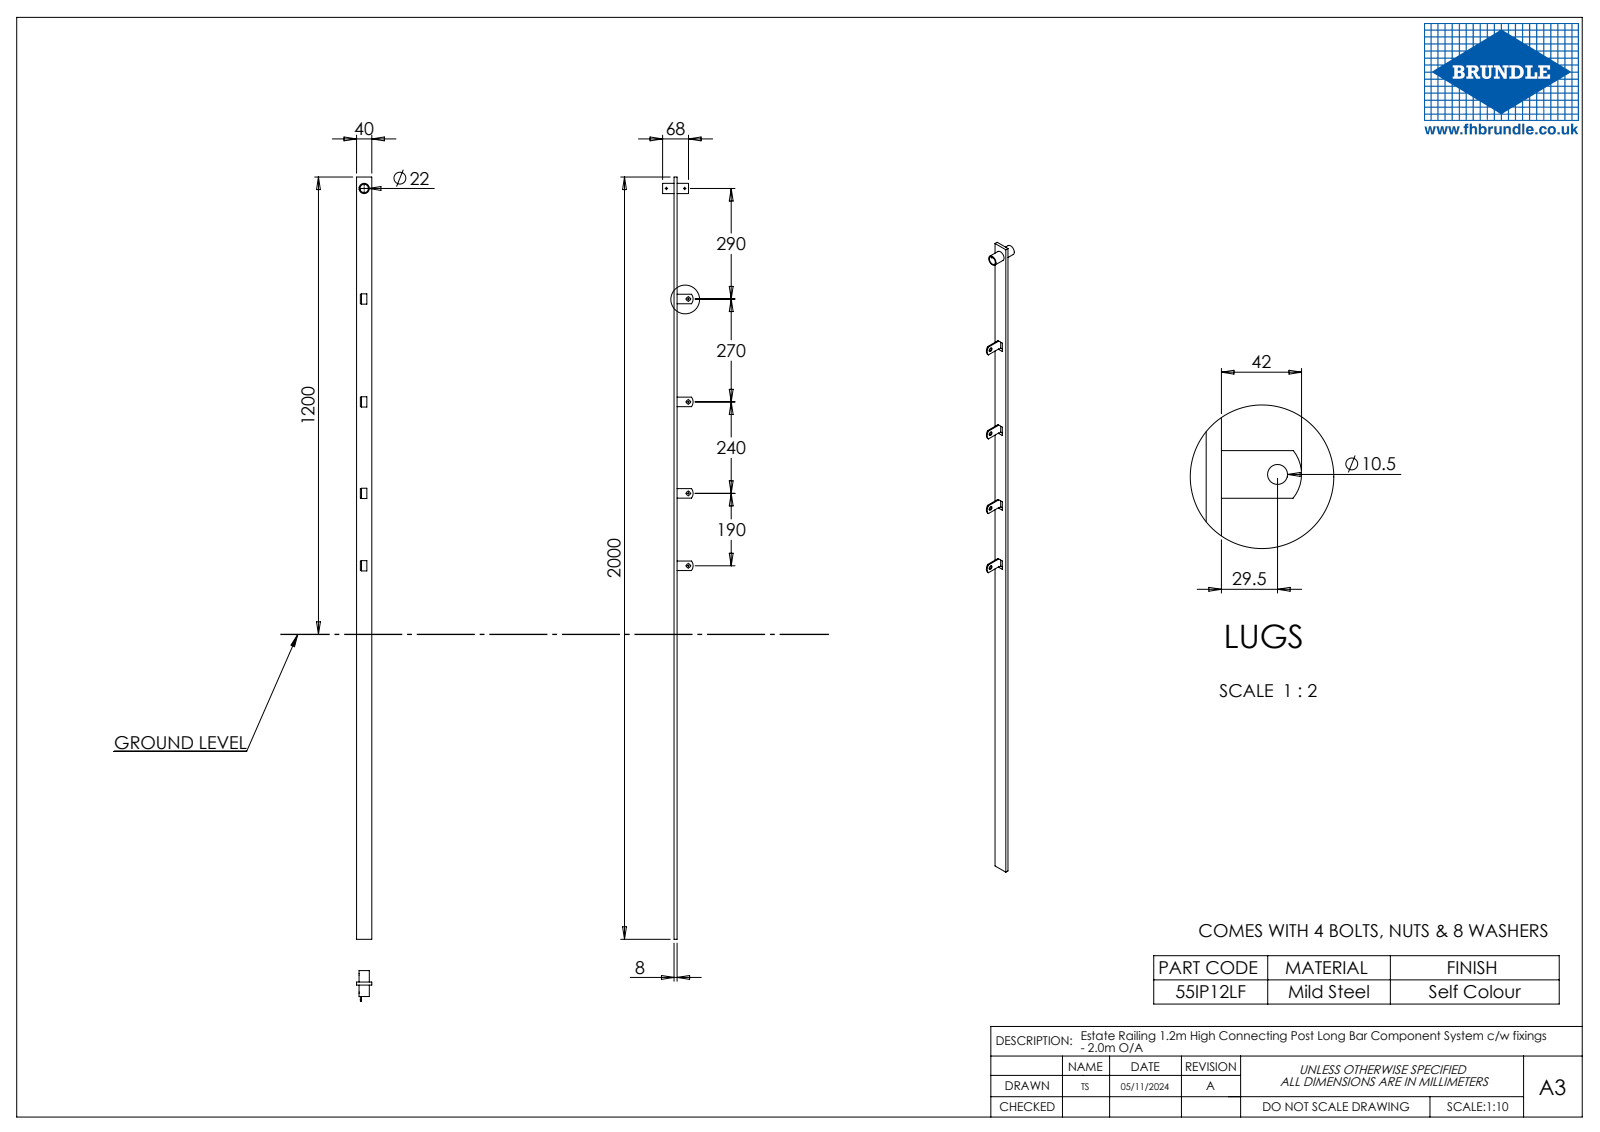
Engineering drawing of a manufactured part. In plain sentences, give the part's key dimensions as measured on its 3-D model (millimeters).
The part is named "65IP12L". Its 3-D file was written by "SolidWorks 2020 (CONFIG_CONTROL_DESIGN)". It is 5 solids with 66 faces: 44 planar, 22 cylindrical and 0 other. Overall it measures 2000 by 81.07 by 40 millimeters. Its volume is 647 257 cubic millimeters and its surface area 210 629 square millimeters. Round holes: 4 of diameter 10.5, 2 of diameter 4, 1 of diameter 22. Round bosses or shafts: 1 of diameter 26.9. Partial cylindrical surfaces (rounded edges, fillets, slot ends): 4 of radius 20. The main face-to-face distances are 8, 40, 27, 13, 30, 3, 10, 1, 26, 14. The hole center spacings are 48, 190, 240, 270, 290.19, 295.84, 430, 510.
